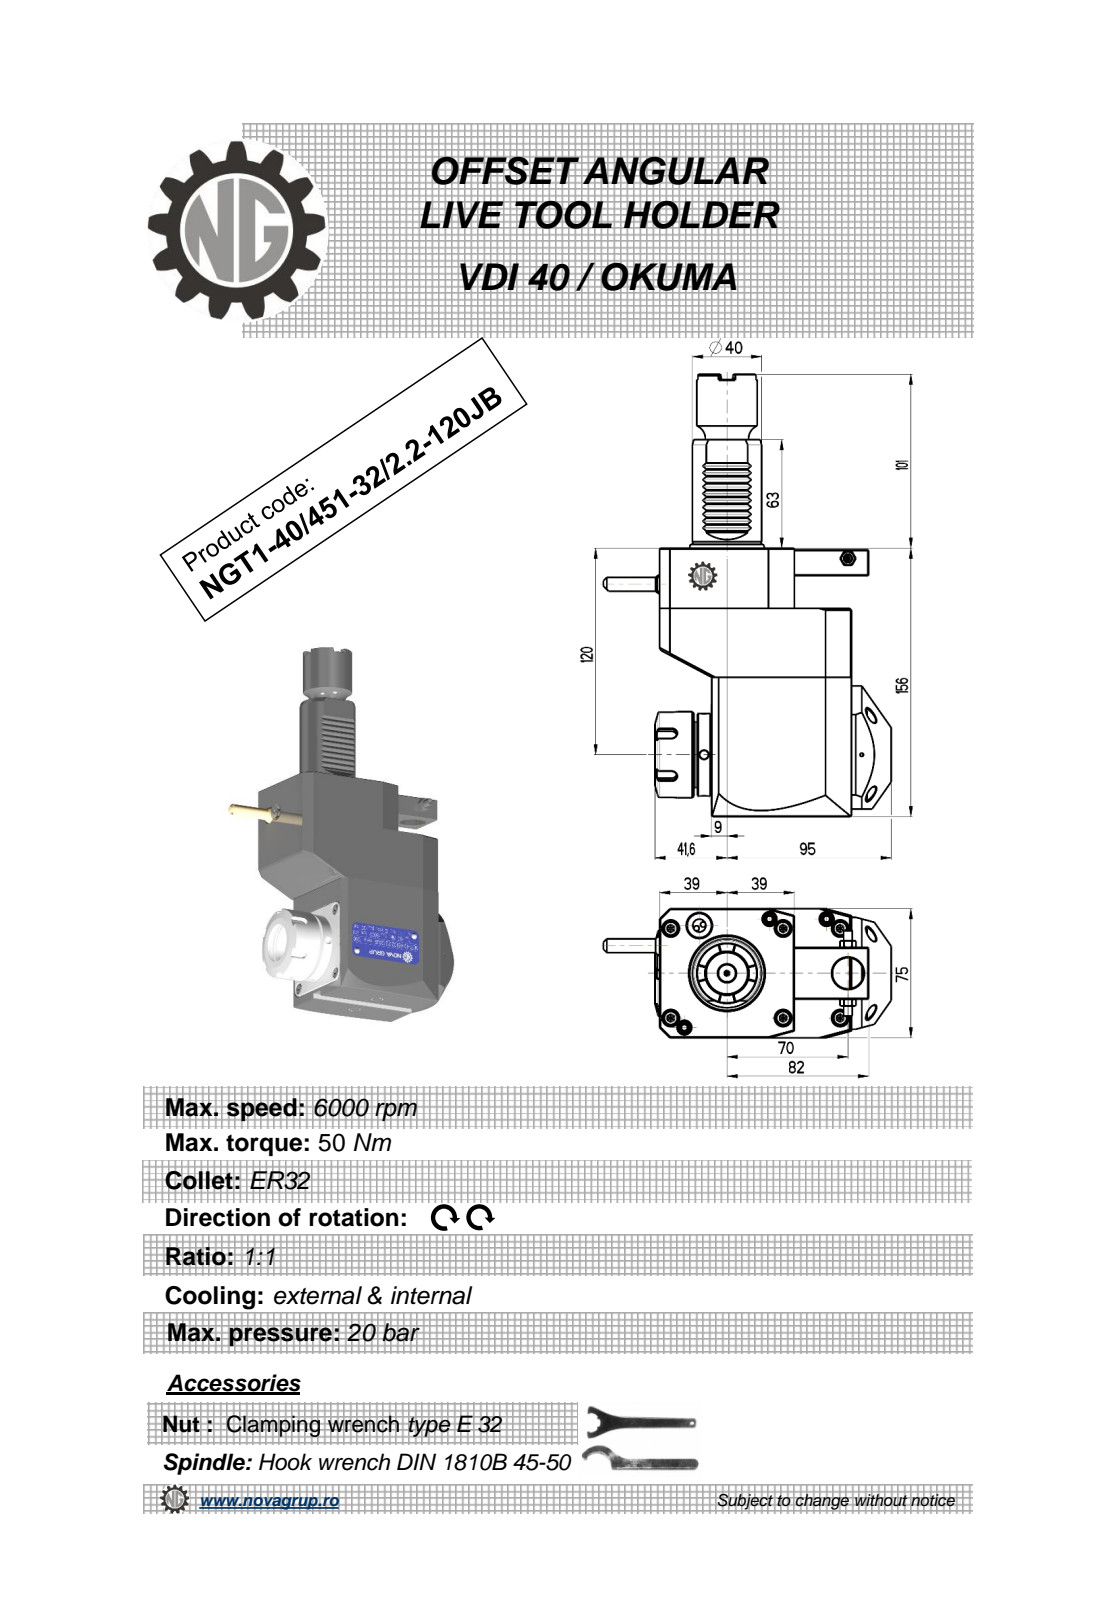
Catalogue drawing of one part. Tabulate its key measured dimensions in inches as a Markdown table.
| quantity | value |
| --- | --- |
| part name | NGT1_40_451_32_2_2_120JB |
| STEP written by | PRO/ENGINEER BY PARAMETRIC TECHNOLOGY CORPORATION, 2010280 (CONFIG_CONTROL_DESIGN) |
| units | inches |
| bodies | 1 solid, 477 faces (217 planar, 95 cylindrical, 165 other) |
| overall size | 10.118 × 6.555 × 3.016 |
| volume | 75.55 in³ |
| surface area | 146.5 in² |
| round holes (diameter × count) | 0.197 × 3, 0.118 × 1, 0.165 × 1, 0.374 × 1, 0.709 × 1, 0.984 × 1, 1.055 × 1, 1.063 × 1 |
| round bosses / shafts (diameter × count) | 1.969 × 1, 1.89 × 1, 1.614 × 1, 1.575 × 1, 1.378 × 1, 1.046 × 1, 0.394 × 1, 0.353 × 1 |
| partial cylindrical surfaces (radius × count) | 0.01 × 12, 0.012 × 10, 0.008 × 6, 0.118 × 5, 0.02 × 1, 1.575 × 1 |
| main face-to-face distances | 2.953, 6.142, 4.37, 1.181, 4.764, 1.378, 1.299, 3.189, 3.071, 1.89 |
| hole center spacings | 0.522, 0.824, 2.756, 3.278, 3.948, 4.429, 5.557 |
